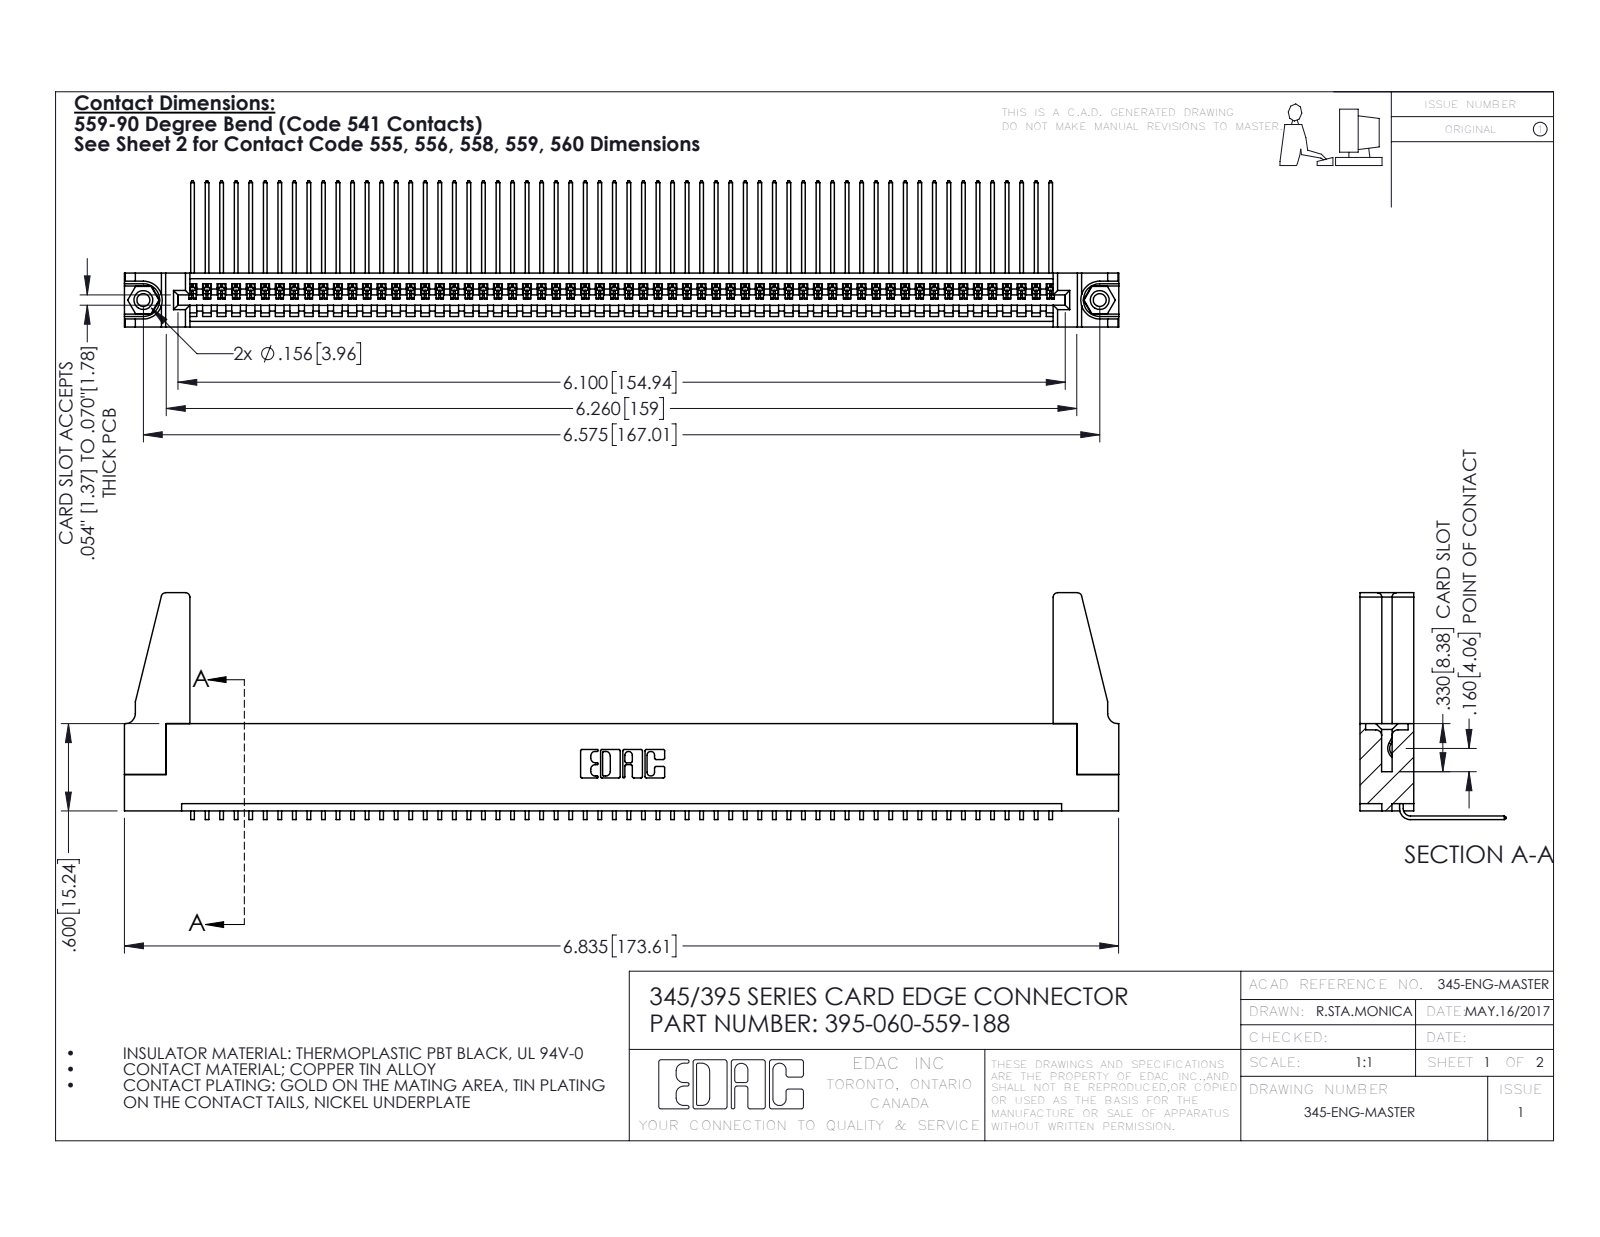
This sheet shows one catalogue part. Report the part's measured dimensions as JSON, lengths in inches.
{"part_name": "395-060-559-188; 345-220-078_345-220-088; 345-250-001_345-250-001-102; 345-292-001_558 559 Tail - 1 (+1 more)", "step_written_by": "SolidWorks 2016 (CONFIG_CONTROL_DESIGN)", "units": "inches", "bodies": {"solids": 65, "faces": 3850, "planar": 2672, "cylindrical": 1162, "other": 16}, "overall_size": [6.836, 1.559, 1.005], "volume_in3": 1.226, "surface_area_in2": 41.74, "round_holes": [[0.089, 2], [0.125, 2], [0.156, 2], [0.064, 1]], "round_bosses_or_shafts": [[0.155, 2]], "partial_cylinders_radius": [[0.006, 120], [0.01, 22], [0.03, 8], [0.007, 6], [0.031, 6], [0.026, 3], [0.031, 2], [0.04, 2]], "face_to_face_distances": [0.072, 0.298, 0.37, 0.2, 0.098, 0.272, 0.025, 0.225, 0.149, 0.072], "hole_center_spacings": [0.27, 6.339, 6.575]}
